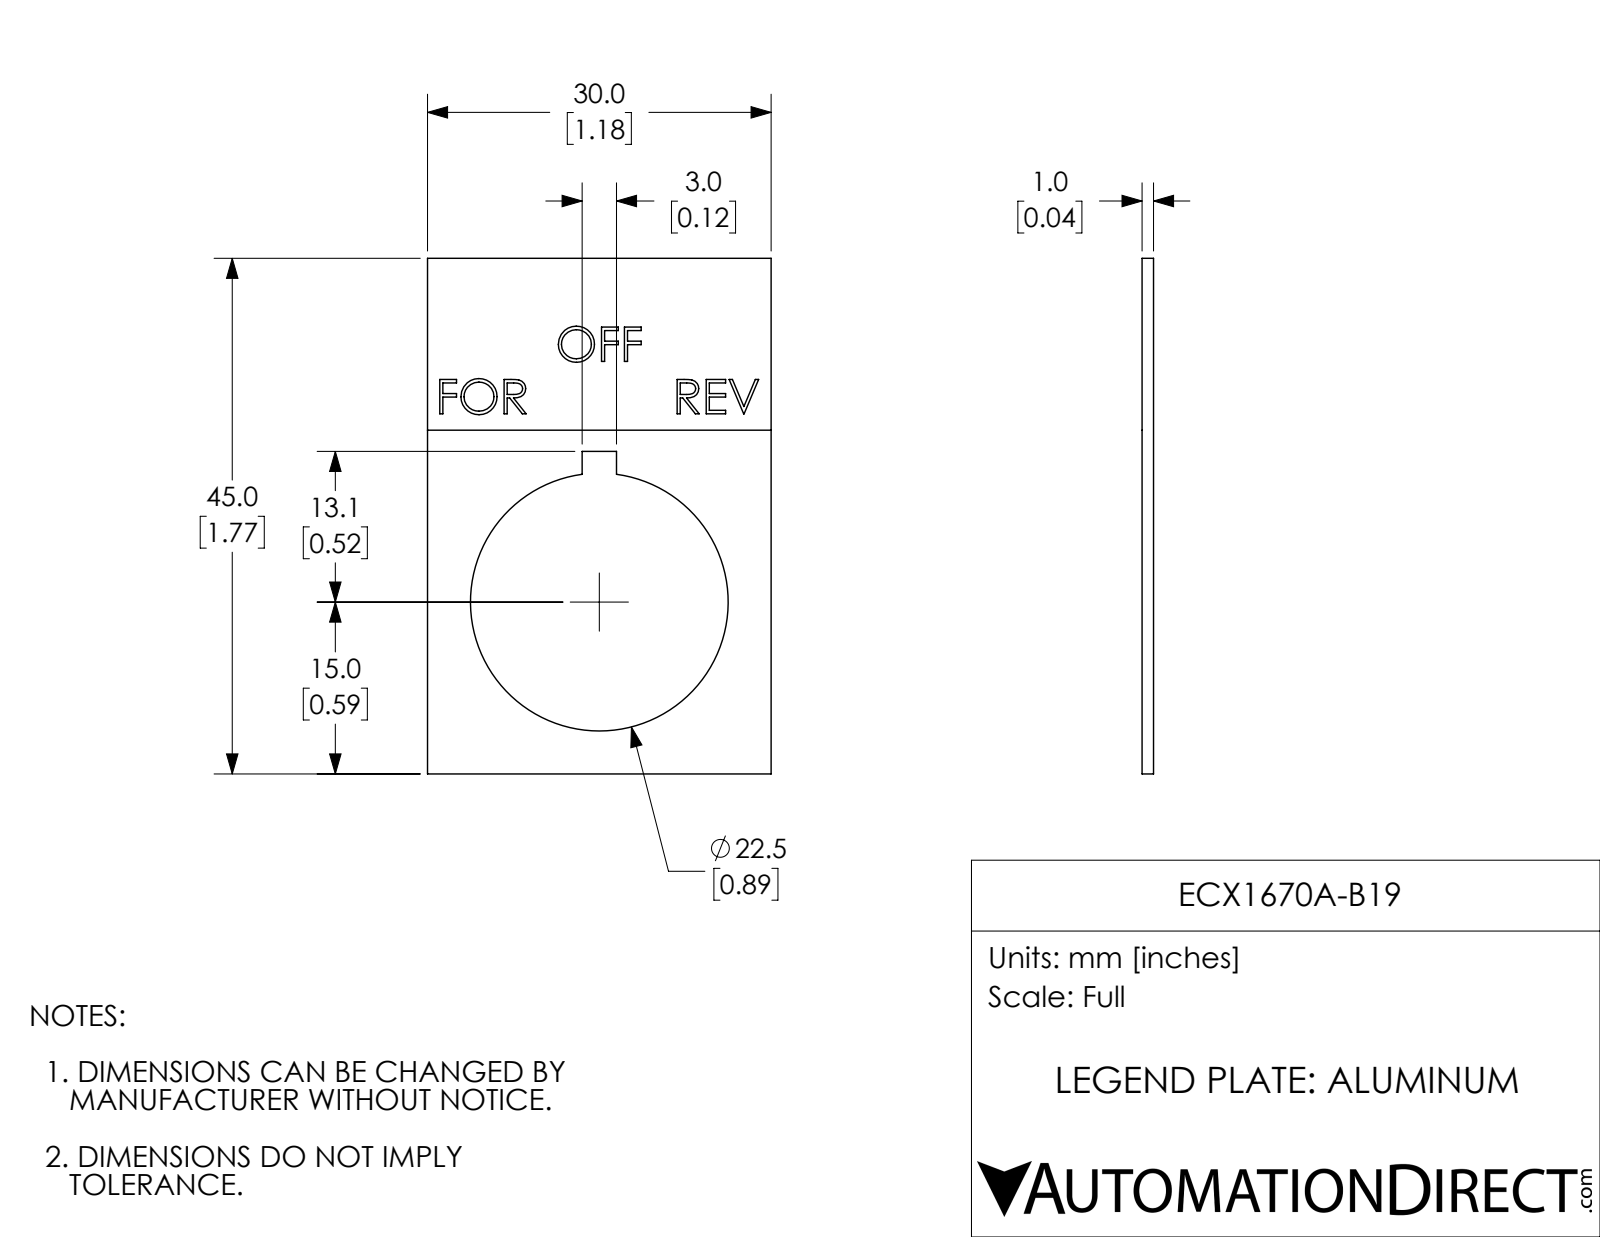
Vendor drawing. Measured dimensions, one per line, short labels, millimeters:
name: ECX1670A-B19
written by: SolidWorks 2017 (AUTOMOTIVE_DESIGN)
unit: mm
bodies: 1 solid, 123 faces (94 planar, 3 cylindrical, 26 other)
size: 45 × 30 × 1
volume: 950 mm³; area: 2 121 mm²
holes: 1× ⌀22.5
face distances: 1, 30, 45, 1, 13.5, 16.5, 28.1, 16.8, 3, 0.3
